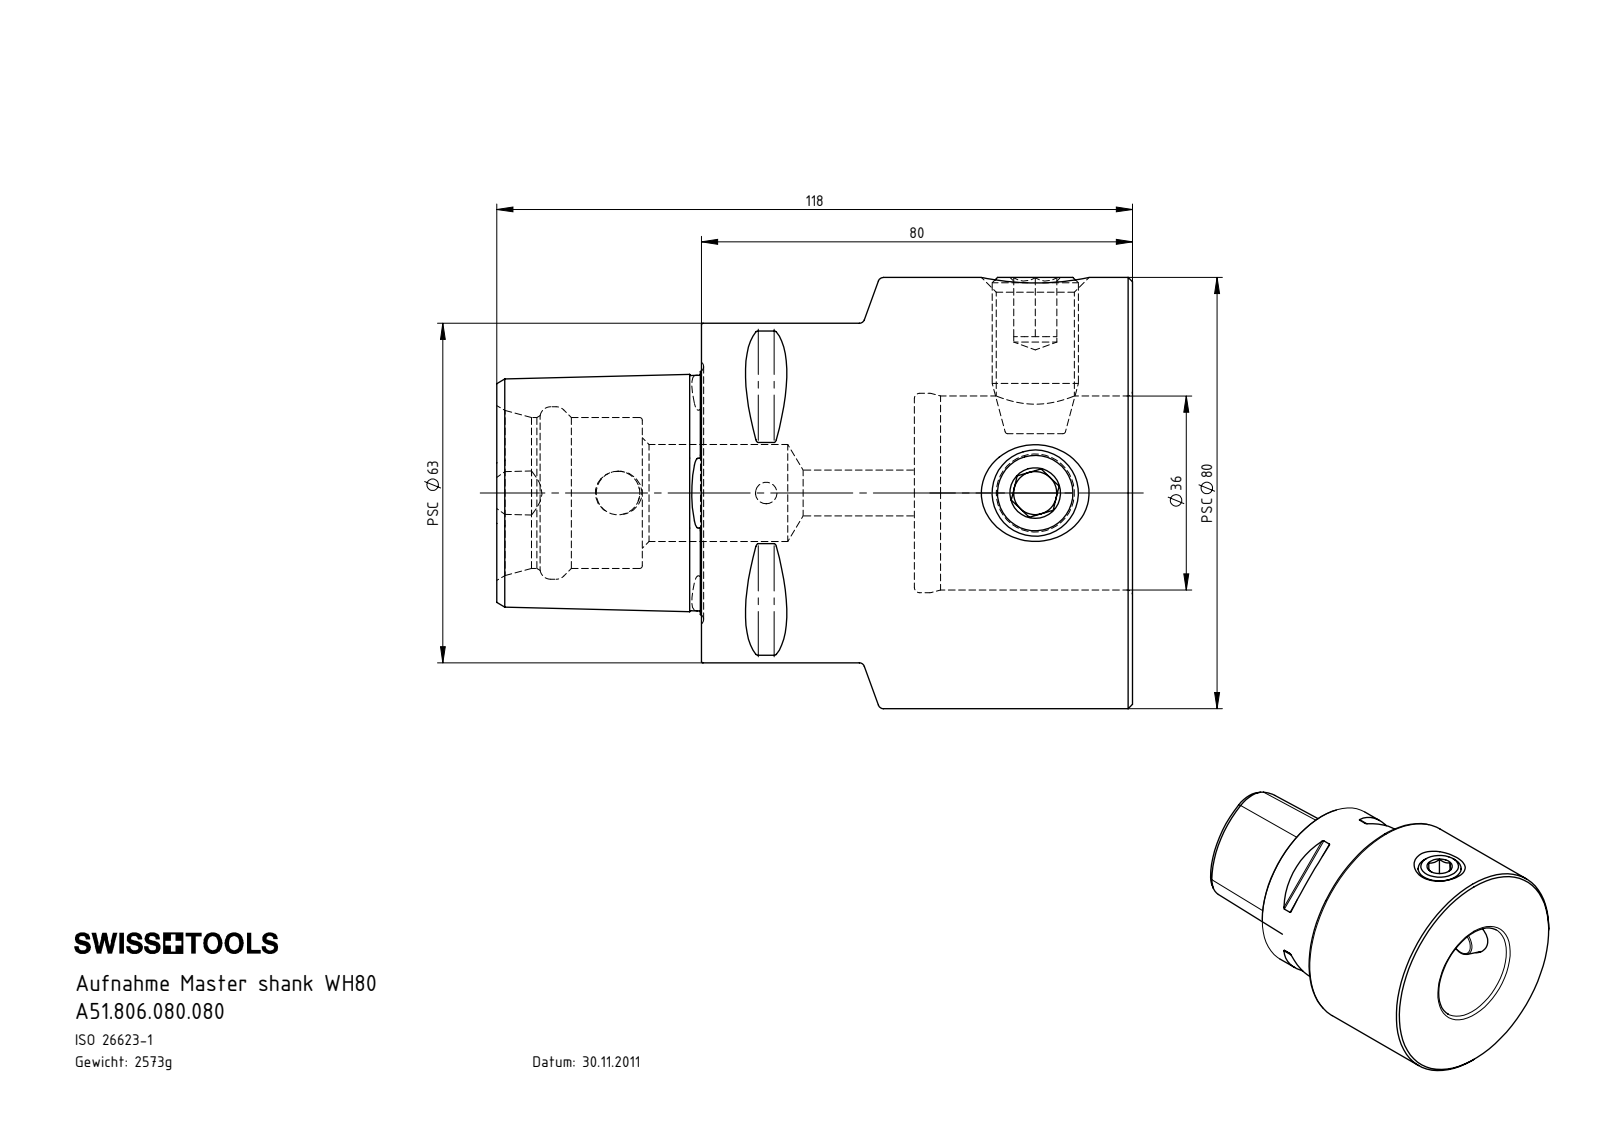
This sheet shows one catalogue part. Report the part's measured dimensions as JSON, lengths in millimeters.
{"part_name": "PS6-WH8.K01.080_B; A51.806.080.080; WH8-ER1.001.029", "step_written_by": "SolidWorks 2022 (AUTOMOTIVE_DESIGN)", "units": "millimeters", "bodies": {"solids": 3, "faces": 204, "planar": 48, "cylindrical": 45, "other": 111}, "overall_size": [118, 80, 80], "volume_mm3": 327715, "surface_area_mm2": 47343, "round_holes": [[8, 2], [14.5, 2], [4, 1], [8.1, 1], [8.5, 1], [18, 1], [28, 1], [32, 1], [36, 1], [37, 1]], "round_bosses_or_shafts": [[16, 2], [80, 1], [63, 1]], "partial_cylinders_radius": [[0.5, 8], [6, 1]], "face_to_face_distances": [80, 39.5, 40.5, 38, 77.5, 118, 24.88, 11, 27, 50.5], "hole_center_spacings": [27.5, 49.95, 77.45]}
